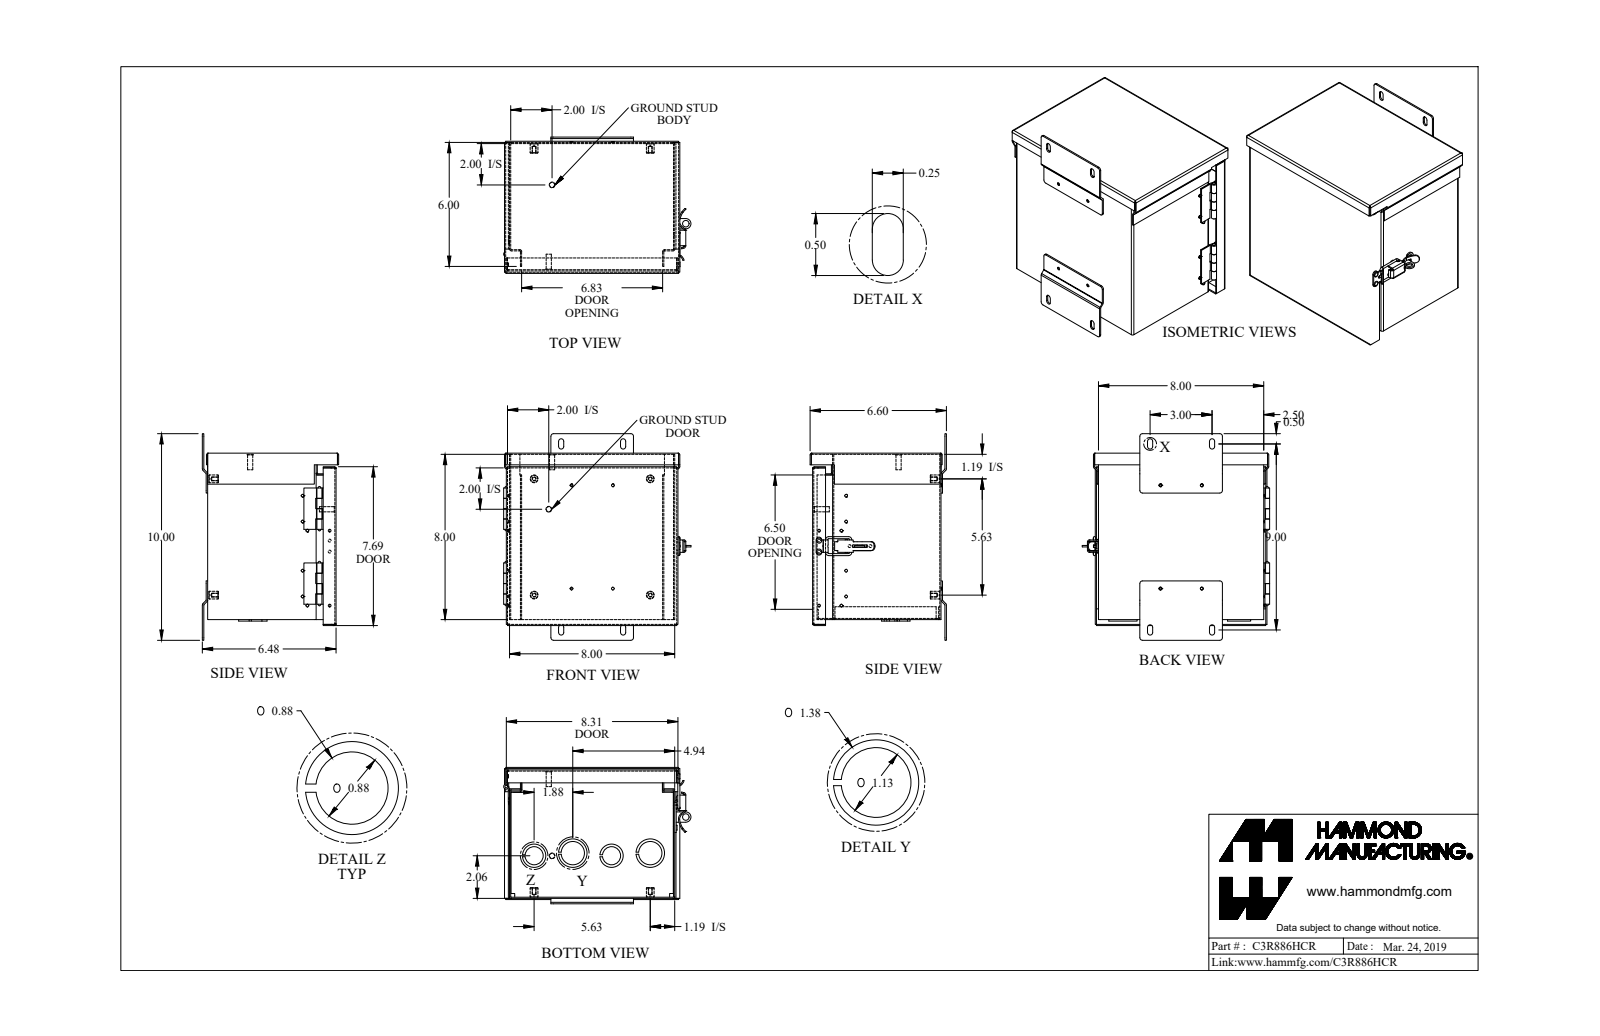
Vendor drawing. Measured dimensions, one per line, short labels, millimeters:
name: C3R886HCR_Default
written by: SolidWorks 2019 (CONFIG_CONTROL_DESIGN)
unit: mm
bodies: 31 solids, 846 faces (496 planar, 295 cylindrical, 55 other)
size: 254 × 230.4 × 167.6
volume: 486 400 mm³; area: 614 500 mm²
holes: 4× ⌀3.5, 4× ⌀3.6, 4× ⌀4, 2× ⌀3.4, 2× ⌀3.7, 1× ⌀3.2, 1× ⌀3.3, 1× ⌀8, 1× ⌀22.2, 1× ⌀22.2, 1× ⌀28.6, 1× ⌀28.6
bosses: 12× ⌀3.3, 4× ⌀9.5, 4× ⌀2.5, 3× ⌀3.2, 2× ⌀28.6, 2× ⌀7.1, 2× ⌀6.4, 2× ⌀3.2
rounds: 28× R0.7, 28× R2.2, 21× R3.2, 6× R0.9, 6× R2.7, 2× R3.4, 1× R1, 1× R1.7
face distances: 1.4, 156.5, 203.2, 201.8, 155, 157.9, 4.7, 204.6, 6.2, 200.3
hole spacings: 142.9, 38, 25.7, 25.7, 46.7, 46.7, 47.8, 50.8
